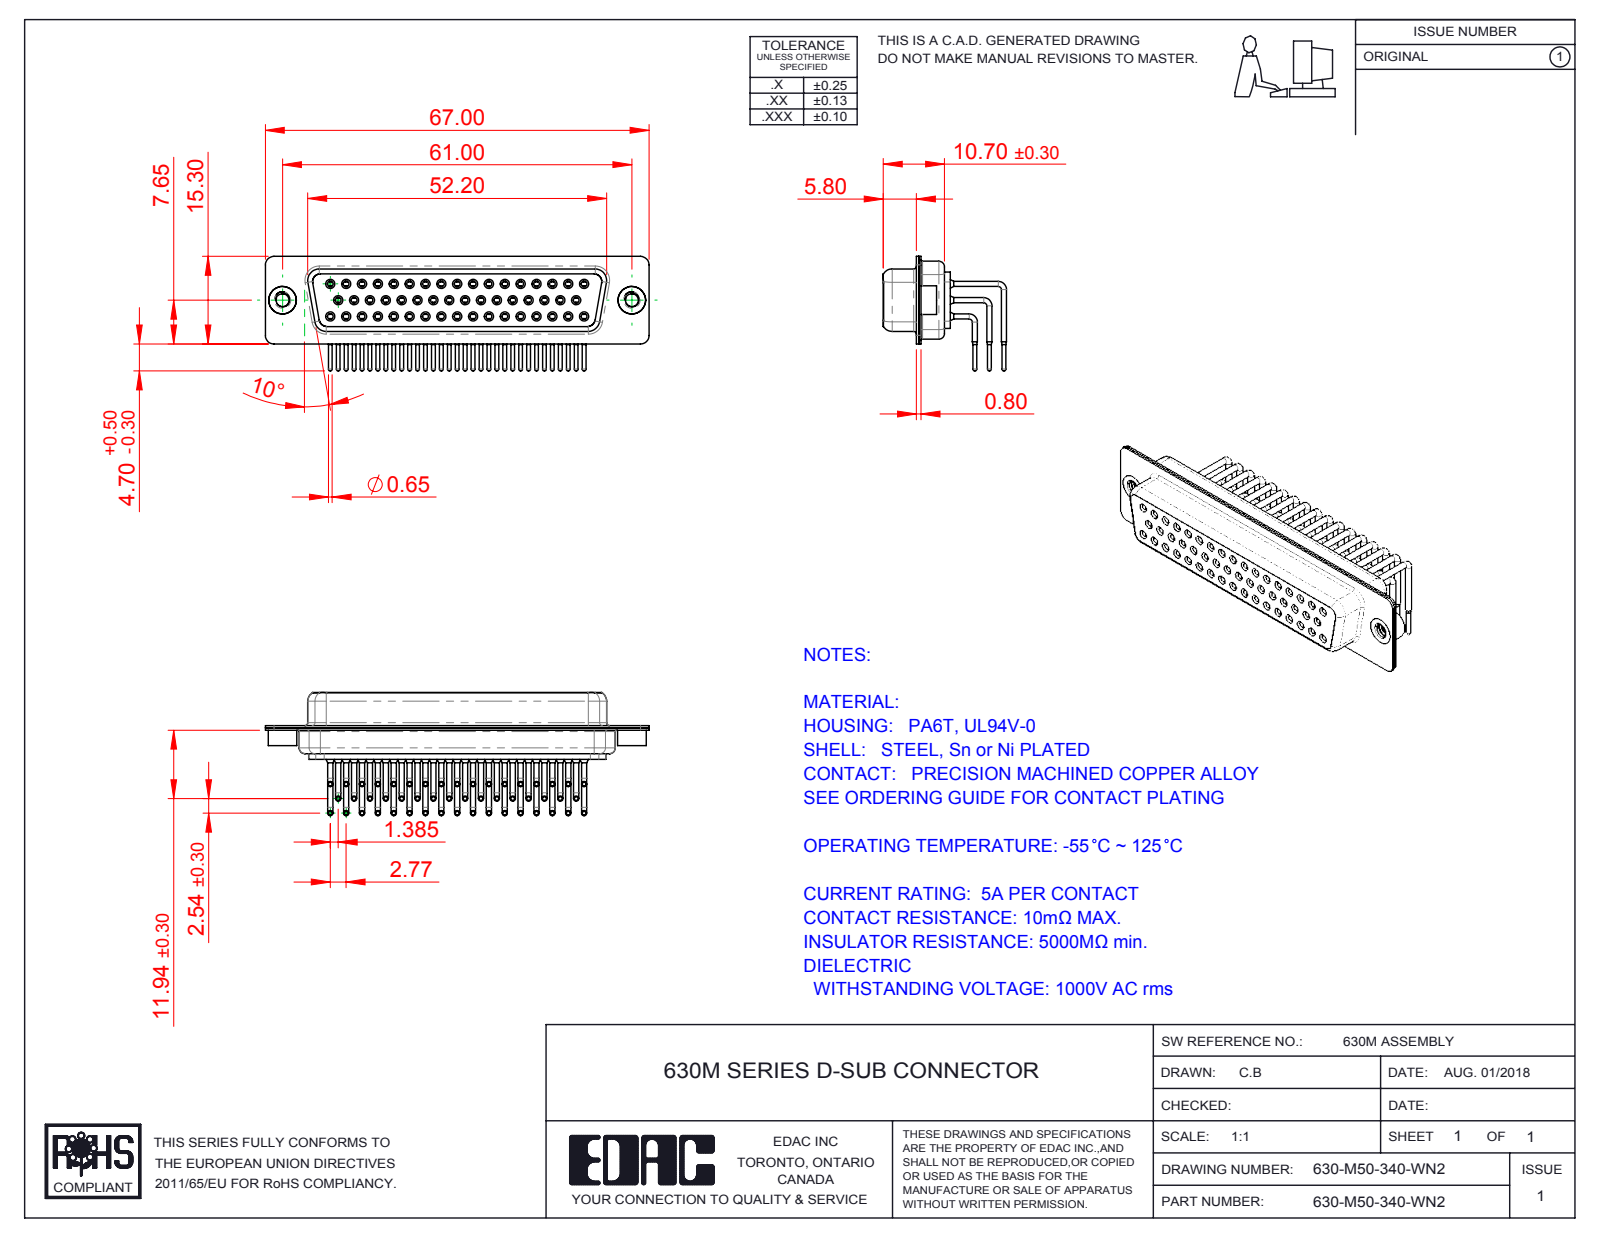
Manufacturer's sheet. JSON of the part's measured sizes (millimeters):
{"part_name": "630M Contact Row 1_50 Contacts; 630M 4-40 Threaded Rivet; 630M Contact Row 2_50 Contacts; 630M Contact Row 3 (+4 more)", "step_written_by": "SolidWorks 2016 (CONFIG_CONTROL_DESIGN)", "units": "millimeters", "bodies": {"solids": 55, "faces": 2929, "planar": 817, "cylindrical": 1287, "other": 825}, "overall_size": [67, 21.53, 20], "volume_mm3": 7020, "surface_area_mm2": 16564, "round_holes": [[1, 50], [1.1, 50], [1.7, 50], [1.8, 50], [2, 50], [2.26, 2], [4, 2], [4.8, 2]], "round_bosses_or_shafts": [[0.9, 100], [1.6, 50], [1.5, 50], [0.65, 50], [5, 2], [4.9, 2]], "partial_cylinders_radius": [[1.5, 16], [2, 12], [1.35, 8], [1.6, 8], [0.25, 4], [0.5, 4], [0.6, 4], [0.65, 4]], "face_to_face_distances": [0.4, 1.35, 11.85, 0.85, 2.2, 5.5, 12.25, 5.9, 10.5, 0.8], "hole_center_spacings": [2.77, 3.16, 5.54, 8.31, 11.08, 13.85, 16.62, 19.39]}
